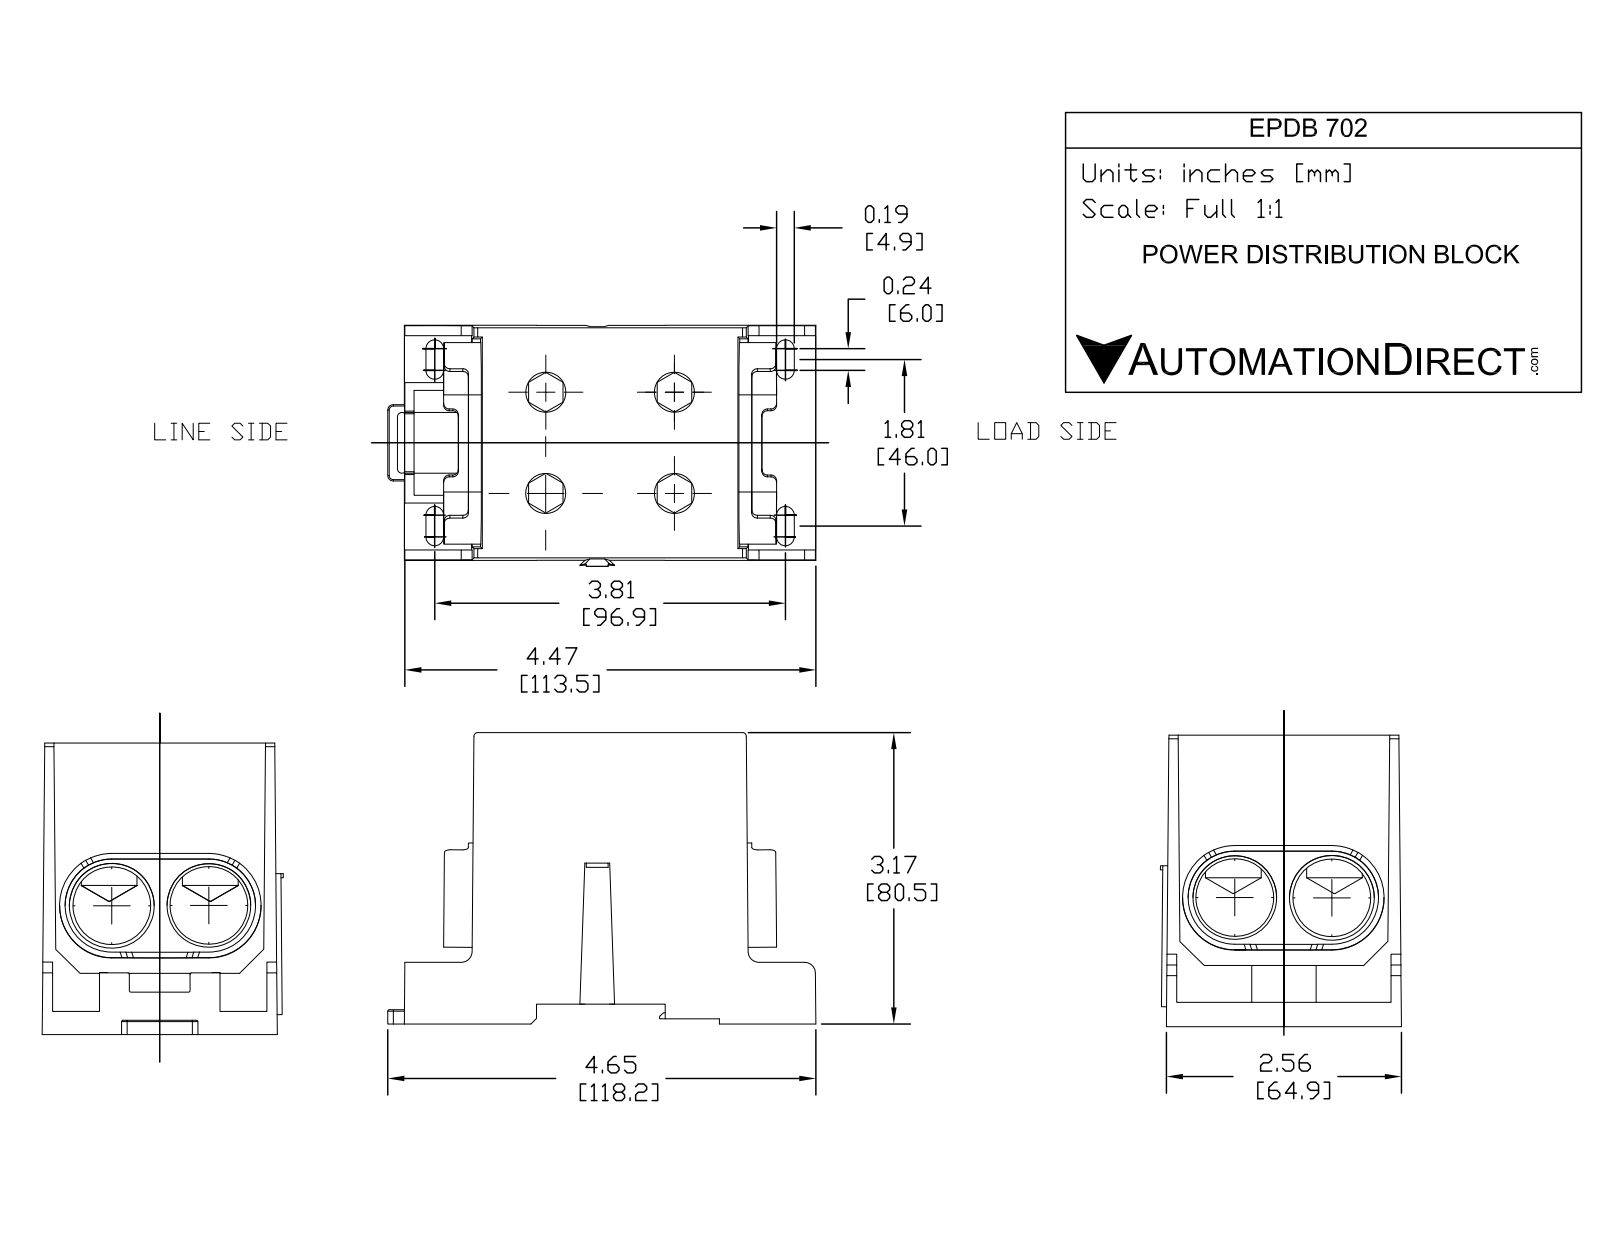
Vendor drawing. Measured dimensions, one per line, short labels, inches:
name: EPDB702
written by: SolidWorks 2011 (CONFIG_CONTROL_DESIGN)
unit: in
bodies: 1 solid, 283 faces (177 planar, 96 cylindrical, 10 other)
size: 4.655 × 3.168 × 2.621
volume: 20.03 in³; area: 91.23 in²
holes: 3× ⌀0.435, 2× ⌀0.845, 2× ⌀0.91, 2× ⌀0.923, 1× ⌀0.435
bosses: 4× ⌀0.606
rounds: 18× R0.06, 8× R0.096, 7× R0.015, 4× R0.508, 4× R0.568, 3× R0.118, 2× R0.04, 2× R0.049
face distances: 3.168, 0.216, 2.952, 0.09, 0.729, 0.819, 0.057, 0.159, 3.111, 0.265
hole spacings: 1.056, 1.1, 1.399, 1.4, 1.78, 1.78
